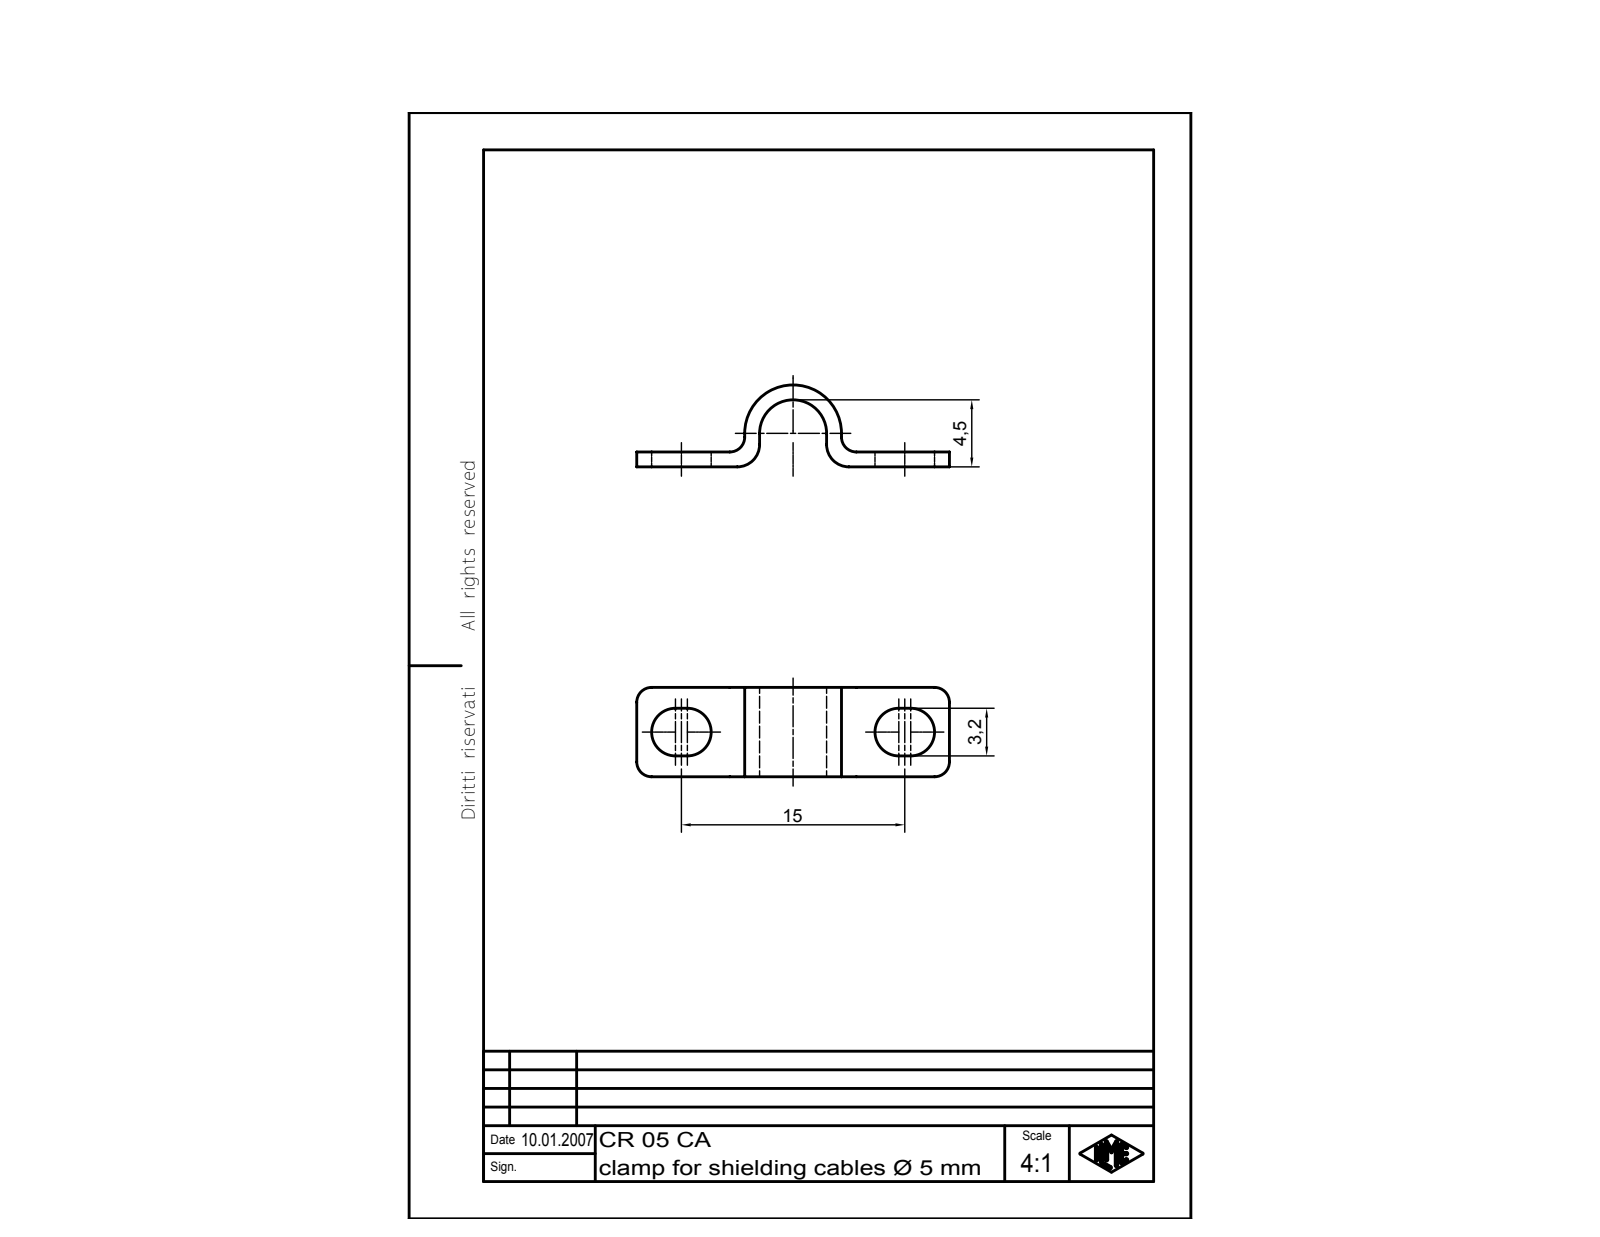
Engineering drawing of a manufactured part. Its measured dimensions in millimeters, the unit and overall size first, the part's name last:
Units: millimetres
Overall size (bounding box): 21 × 6 × 5.5
Partial cylindrical surfaces — rounded edges, fillets, slot ends (radius × count): R1 ×6, R1.5 ×2, R1.6 ×2, R2.25 ×1, R3.25 ×1
Main face-to-face distances: 1, 6, 8.25, 12.75, 4.5, 21, 7.25, 13.75, 5.5, 1.4
Volume: 141 mm³ · Surface area: 362 mm²
Bodies: 1 solid, 34 faces (14 planar, 16 cylindrical, 4 other)
Part name (STEP PRODUCT): CR 05 CA
STEP written by: Autodesk Inventor 7 (AUTOMOTIVE_DESIGN)
